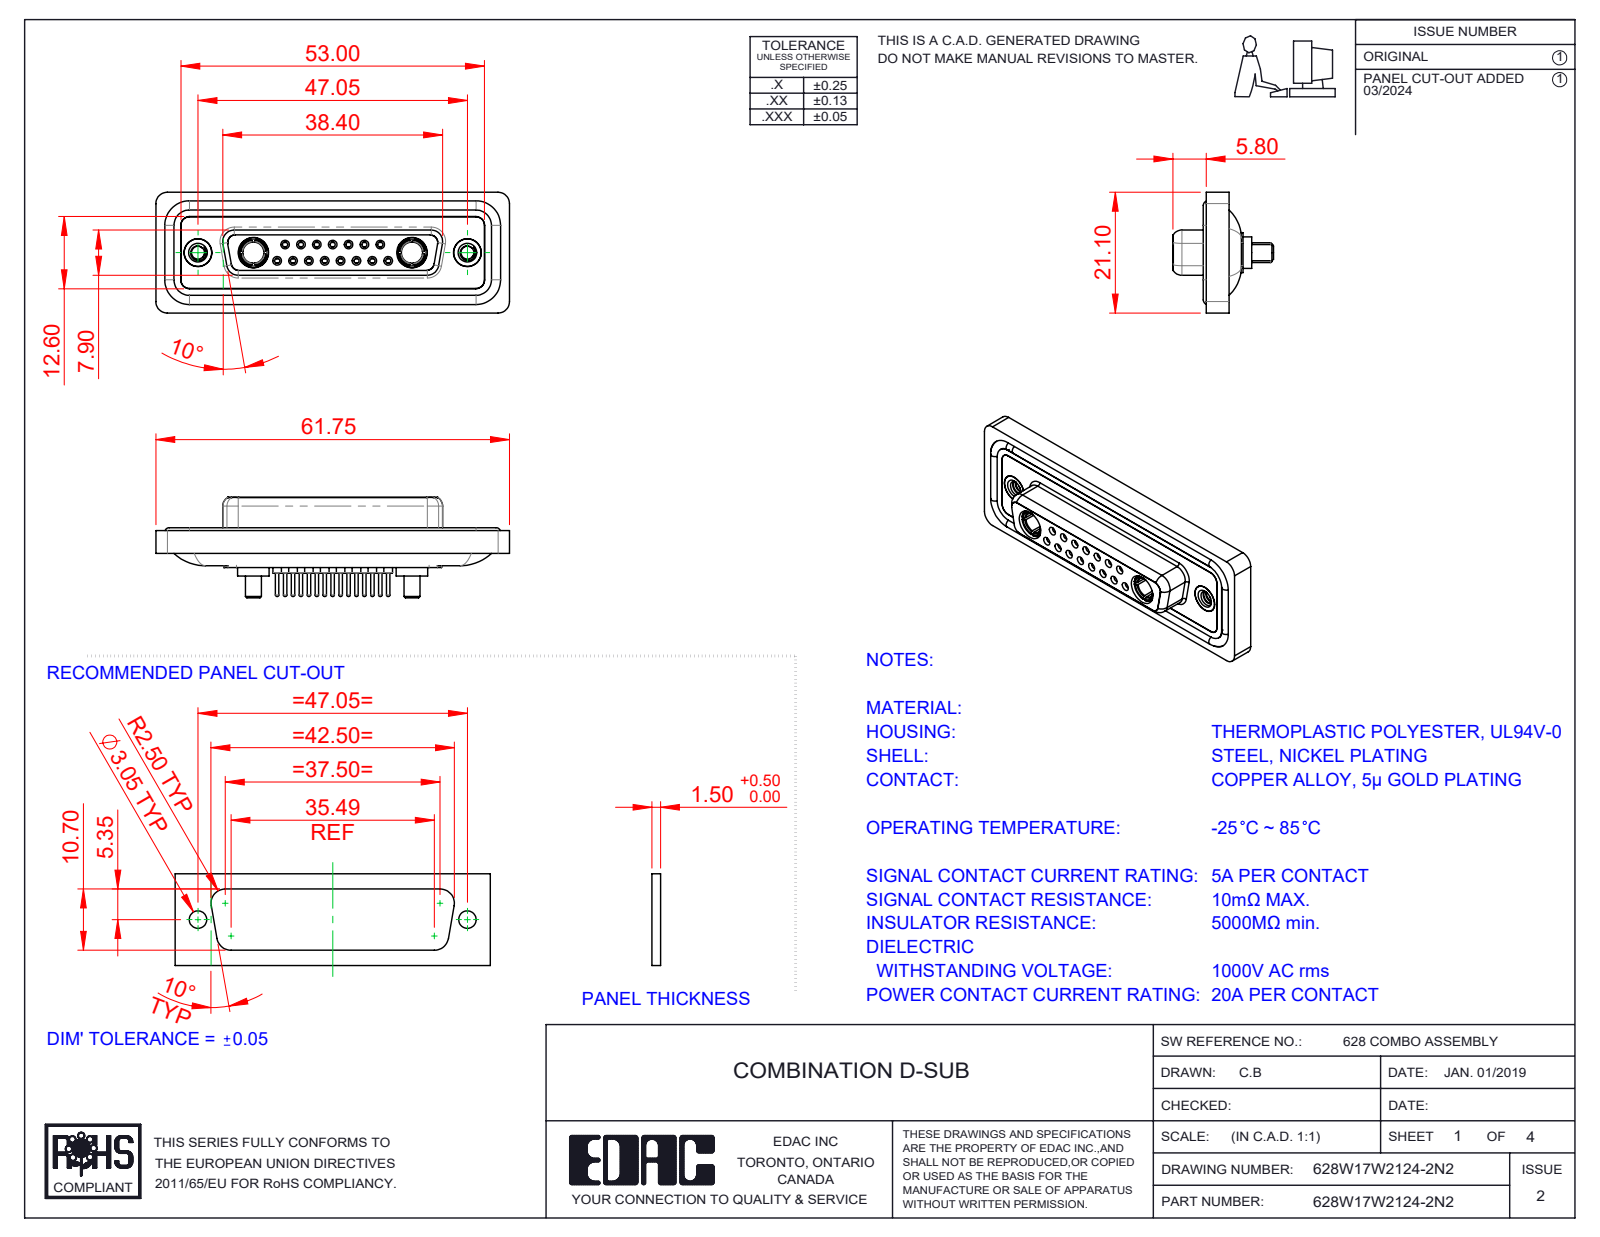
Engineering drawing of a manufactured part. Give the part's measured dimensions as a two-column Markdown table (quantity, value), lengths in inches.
| quantity | value |
| --- | --- |
| part name | Power Socket_20A S; 628Combo Shell Rear_25 Contacts; 628Combo Shell Front_25 Contacts; 628Combo Waterproof Housing_25 Contacts (+5 more) |
| STEP written by | SolidWorks 2023 (CONFIG_CONTROL_DESIGN) |
| units | inches |
| bodies | 26 solids, 1359 faces (388 planar, 519 cylindrical, 452 other) |
| overall size | 2.431 × 0.831 × 0.691 |
| volume | 0.508 in³ |
| surface area | 21.48 in² |
| round holes (diameter × count) | 0.035 × 15, 0.043 × 15, 0.059 × 15, 0.079 × 15, 0.063 × 8, 0.067 × 7, 0.191 × 4, 0.089 × 2, 0.146 × 2, 0.157 × 2, 0.159 × 2, 0.197 × 2 |
| round bosses / shafts (diameter × count) | 0.087 × 15, 0.024 × 15, 0.063 × 11, 0.217 × 2, 0.205 × 2, 0.195 × 2, 0.195 × 2, 0.189 × 2 |
| partial cylindrical surfaces (radius × count) | 0.059 × 22, 0.079 × 18, 0.053 × 8, 0.063 × 8, 0.01 × 4, 0.02 × 4, 0.024 × 4, 0.026 × 4 |
| main face-to-face distances | 0.016, 0.071, 0.293, 0.222, 0.26, 0.02, 0.278, 0.063, 0.114, 0.043 |
| hole center spacings | 0.124, 0.109, 0.327, 0.218, 0.198, 0.198, 0.295, 0.436 |
